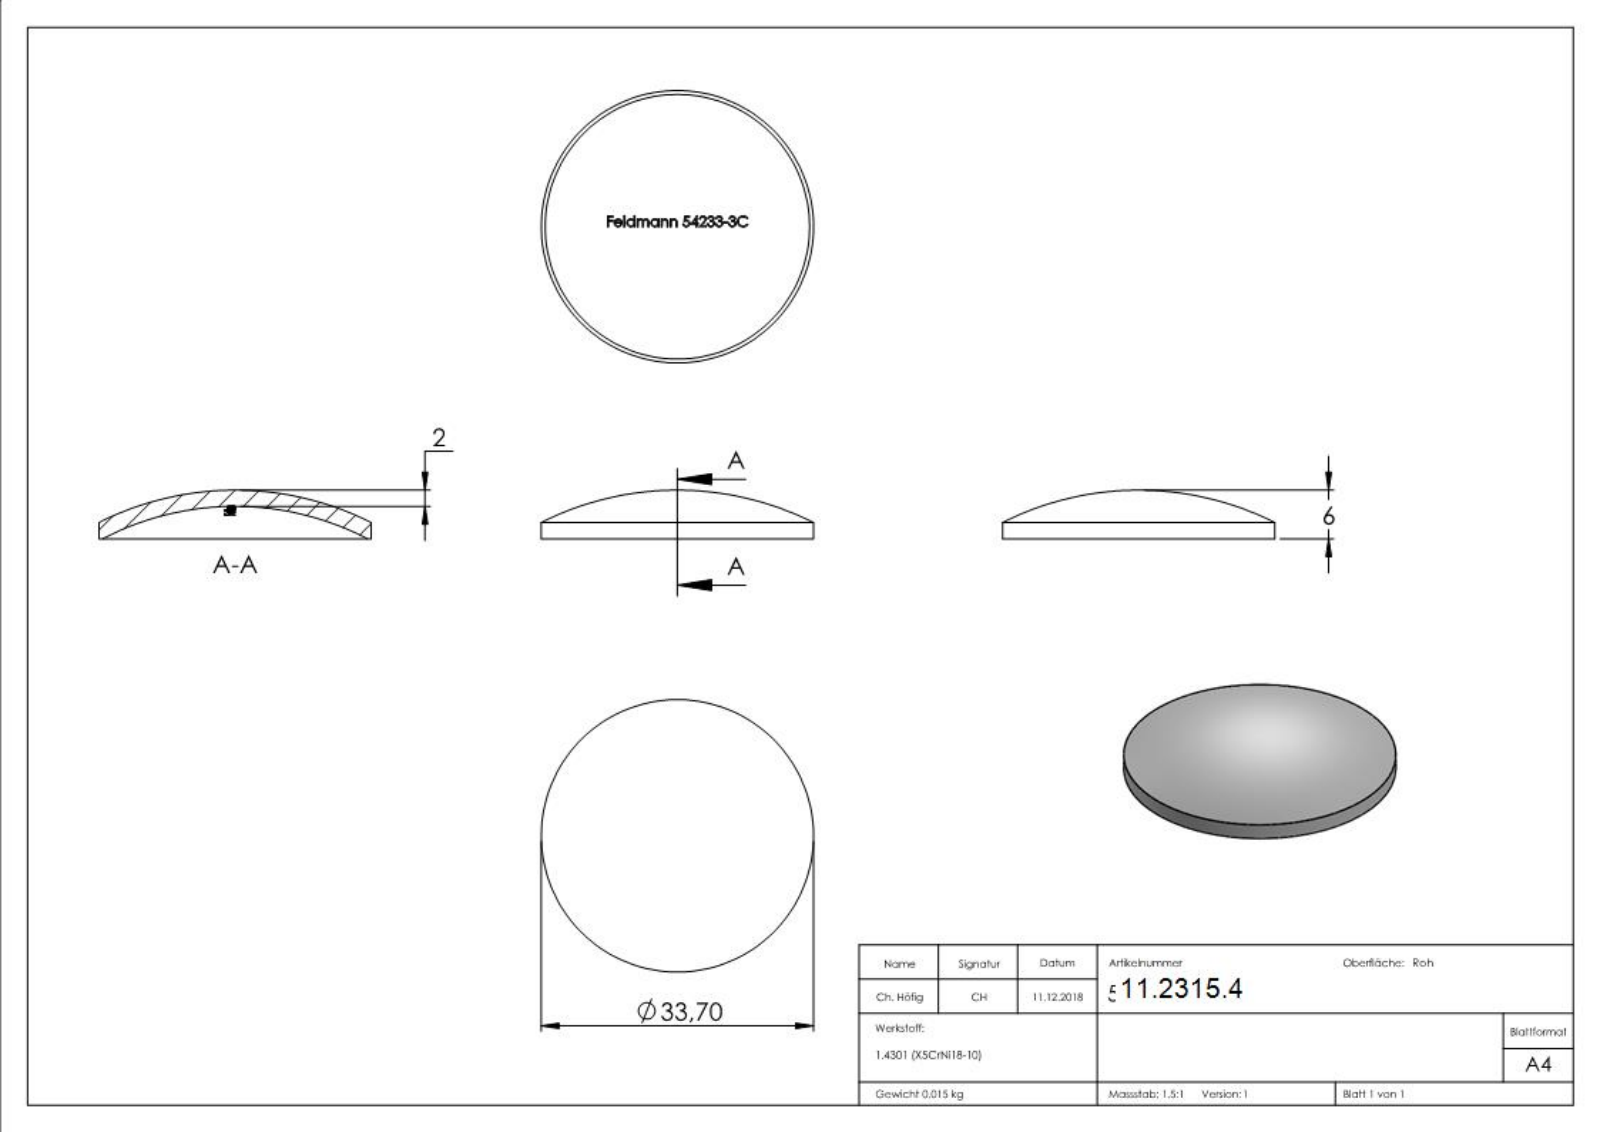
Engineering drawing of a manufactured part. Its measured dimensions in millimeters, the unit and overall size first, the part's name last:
Units: millimetres
Overall size (bounding box): 33.7 × 33.7 × 6
Round bosses / shafts (diameter × count): ⌀33.7 ×1
Main face-to-face distances: 0.39, 2.97, 1.12, 2.02, 0.44, 0.88, 1.25, 8.92, 1.64, 4.09
Volume: 1 884 mm³ · Surface area: 2 105 mm²
Bodies: 1 solid, 248 faces (95 planar, 2 cylindrical, 151 other)
Part name (STEP PRODUCT): 54233-3C
STEP written by: SolidWorks 2015 (CONFIG_CONTROL_DESIGN)
